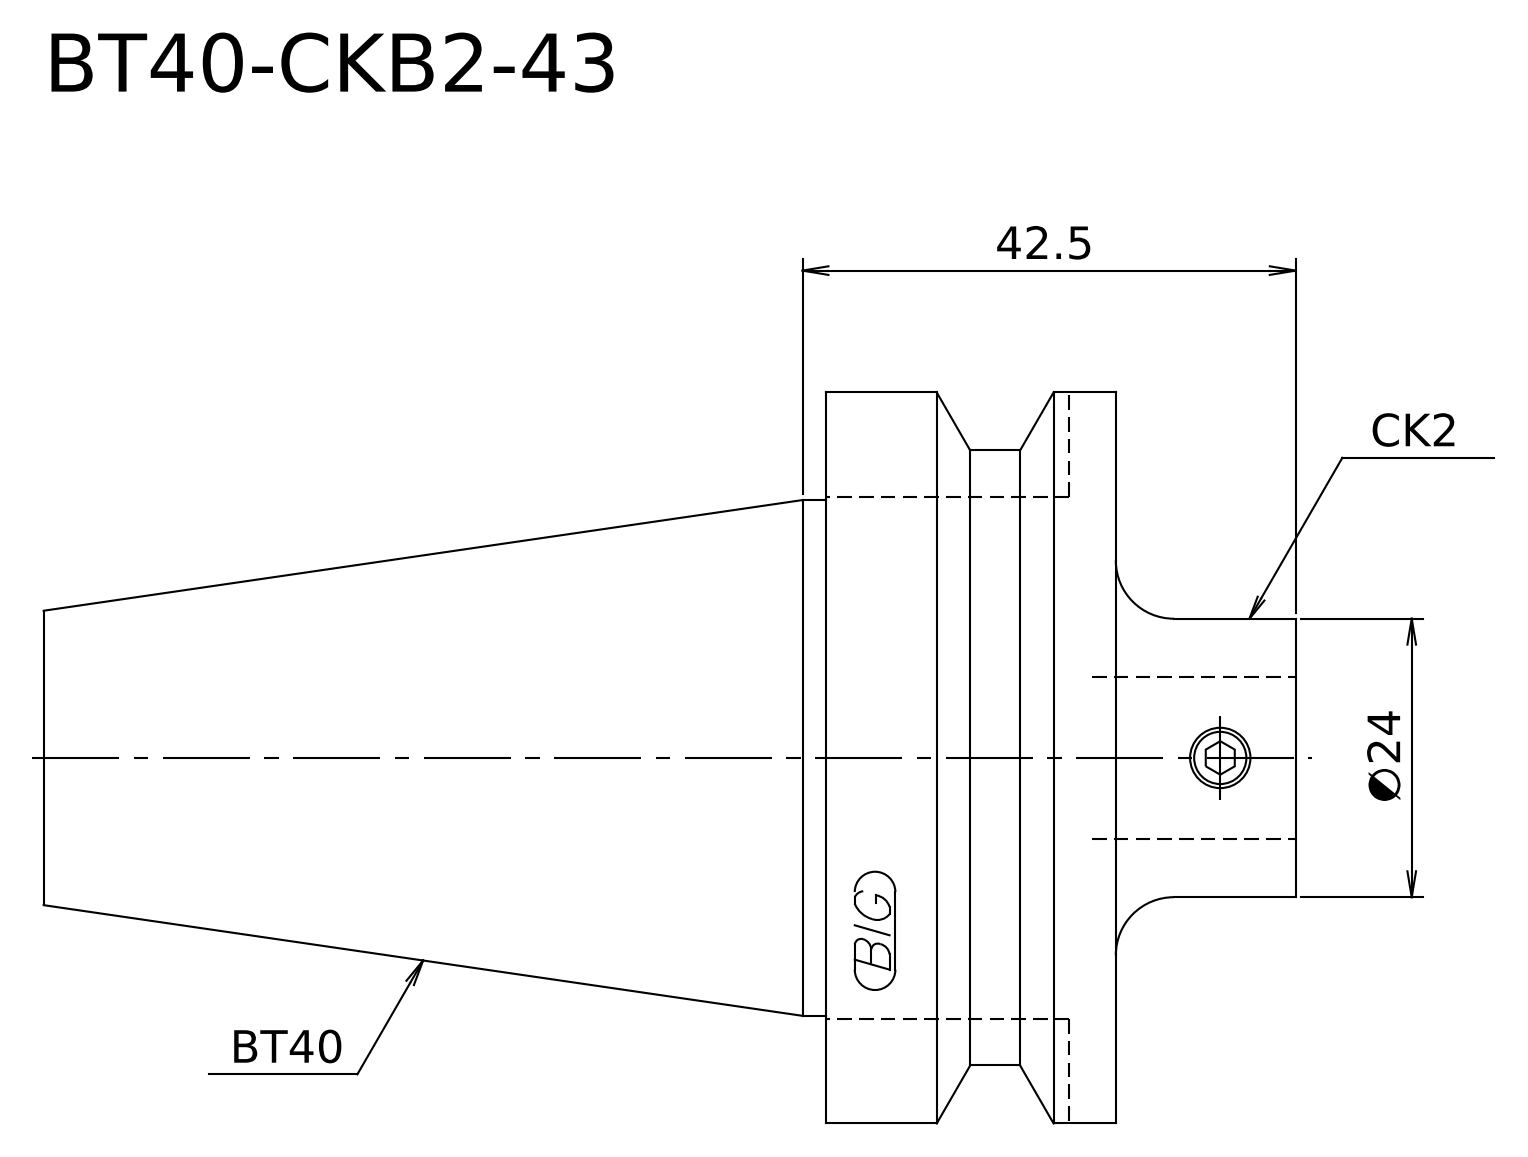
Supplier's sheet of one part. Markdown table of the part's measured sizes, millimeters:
| quantity | value |
| --- | --- |
| STEP written by | Kubotek KeyCreator V8.5.1 (14335) (CONFIG_CONTROL_DESIGN) |
| units | millimeters |
| bodies | 1 solid, 14 faces (4 planar, 5 cylindrical, 5 other) |
| overall size | 107.9 × 63 × 63 |
| volume | 146 709 mm³ |
| surface area | 19 440 mm² |
| round bosses / shafts (diameter × count) | 63 × 1, 53 × 1, 44.45 × 1, 24 × 1 |
| main face-to-face distances | 25, 92.4, 67.4, 15.5, 40.5, 107.9 |
